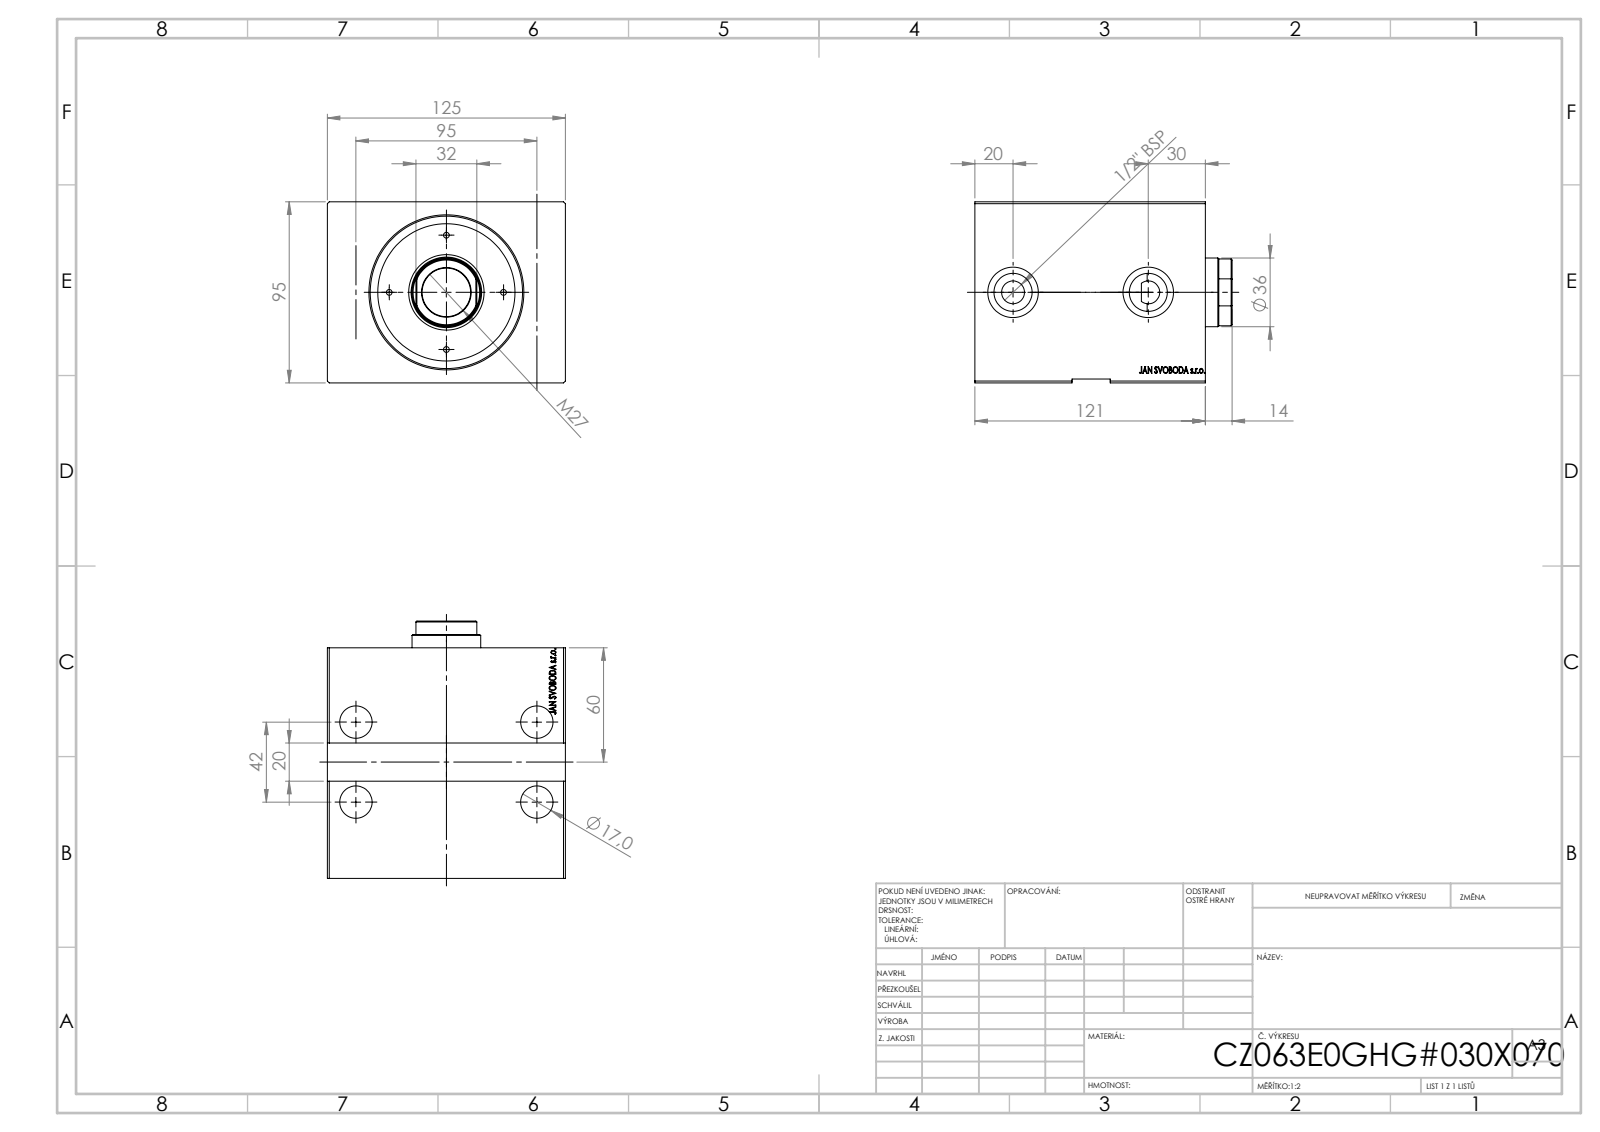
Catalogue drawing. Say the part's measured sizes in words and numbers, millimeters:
Its 3-D file was written by "SolidWorks 2019 (CONFIG_CONTROL_DESIGN)". It is 1 solid with 795 faces: 387 planar, 26 cylindrical and 382 other. Overall it measures 125 by 121 by 95 millimeters. Its volume is 843 626 cubic millimeters and its surface area 121 236 square millimeters. Round holes: 4 of diameter 17, 2 of diameter 20, 2 of diameter 26.5, 1 of diameter 12, 1 of diameter 36, 1 of diameter 63, 1 of diameter 80. Partial cylindrical surfaces (rounded edges, fillets, slot ends): 1 of radius 6. The main face-to-face distances are 95, 125, 121, 102.5, 18.5, 2, 93, 91, 11.5, 30. The hole center spacings are 42, 95, 103.87, 71.
